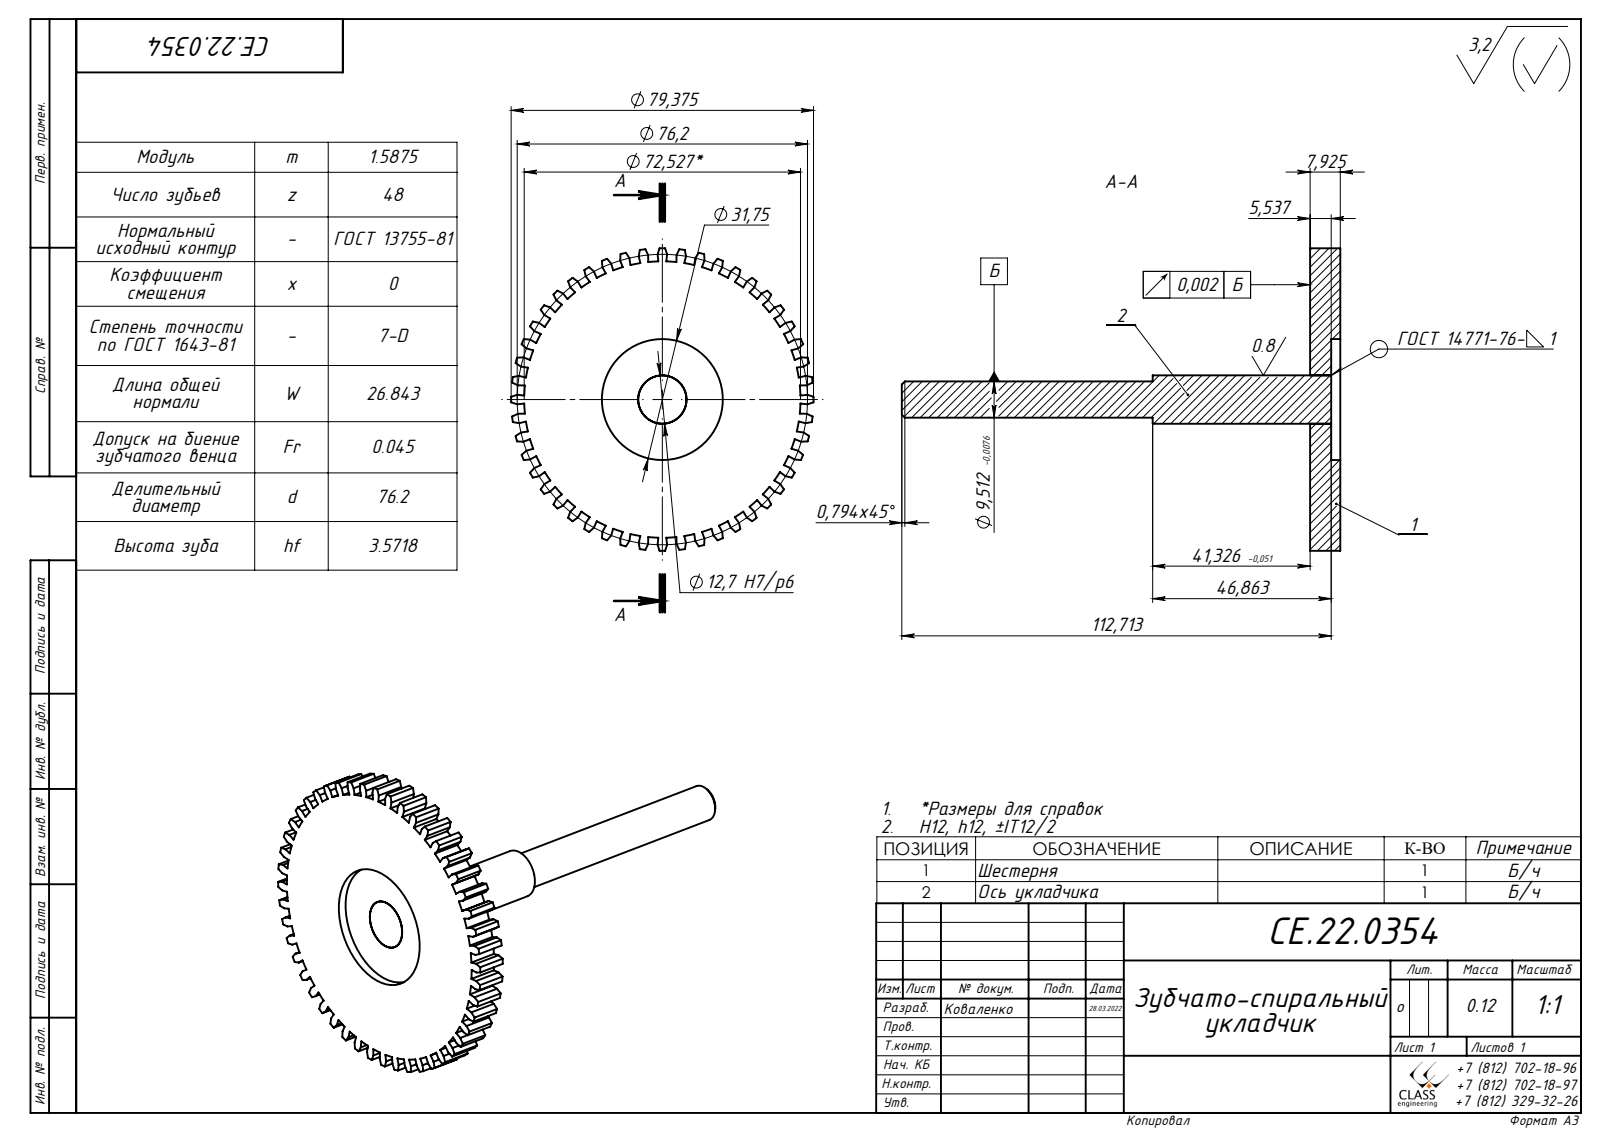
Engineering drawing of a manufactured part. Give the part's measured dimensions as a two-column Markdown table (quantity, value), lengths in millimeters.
| quantity | value |
| --- | --- |
| part name | Ось укладчика 3H420-163.02; Зубчато спиральный укладчик (CE.22.0354) |
| STEP written by | SolidWorks 2020 (AUTOMOTIVE_DESIGN) |
| units | millimeters |
| bodies | 2 solids, 305 faces (198 planar, 105 cylindrical, 2 other) |
| overall size | 115.1 × 79.38 × 79.38 |
| volume | 43 555 mm³ |
| surface area | 17 504 mm² |
| round holes (diameter × count) | 12.7 × 1, 31.75 × 1 |
| round bosses / shafts (diameter × count) | 9.51 × 1 |
| partial cylindrical surfaces (radius × count) | 36.26 × 1, 39.69 × 1, 39.69 × 1 |
| main face-to-face distances | 7.92, 2.39, 5.53, 5.9, 25.38, 5.96, 25.4, 25.42, 5.94, 5.92 |
